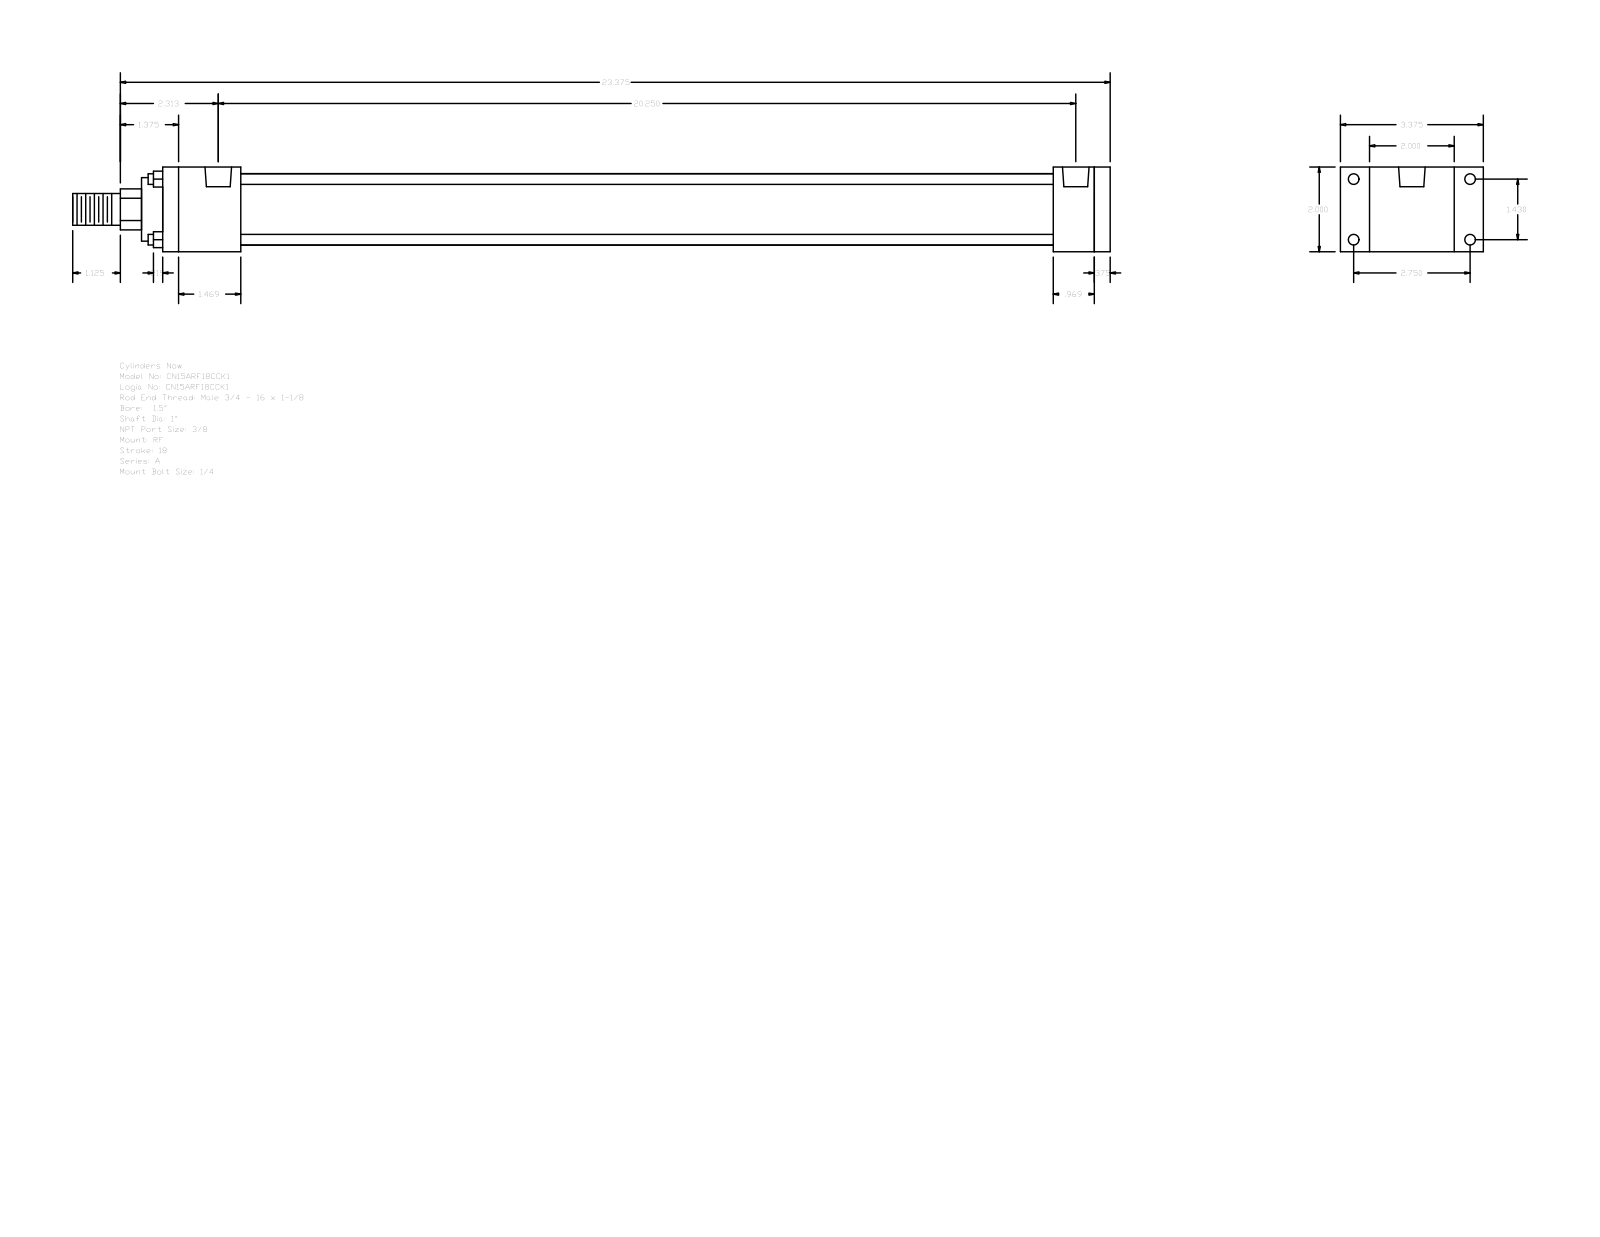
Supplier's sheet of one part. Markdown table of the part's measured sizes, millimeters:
| quantity | value |
| --- | --- |
| part name | A_RF__0150_1 |
| STEP written by | GSSL Pune (CONFIG_CONTROL_DESIGN) |
| units | millimeters |
| bodies | 0 solids, 92 faces (64 planar, 28 cylindrical, 0 other) |
| overall size | 622.3 × 85.72 × 50.8 |
| round holes (diameter × count) | 5.56 × 4, 6.35 × 4, 15.93 × 2 |
| round bosses / shafts (diameter × count) | 6.35 × 4, 42.93 × 1, 38.1 × 1, 25.4 × 1, 19.05 × 1 |
| partial cylindrical surfaces (radius × count) | 12.29 × 1 |
| main face-to-face distances | 50.8, 9.53, 558.8, 568.33, 534.19, 24.61, 34.14, 46.83, 487.36, 511.97 |
| hole center spacings | 3.97, 36.32, 69.84, 78.72, 506.41, 510.38, 514.35 |
